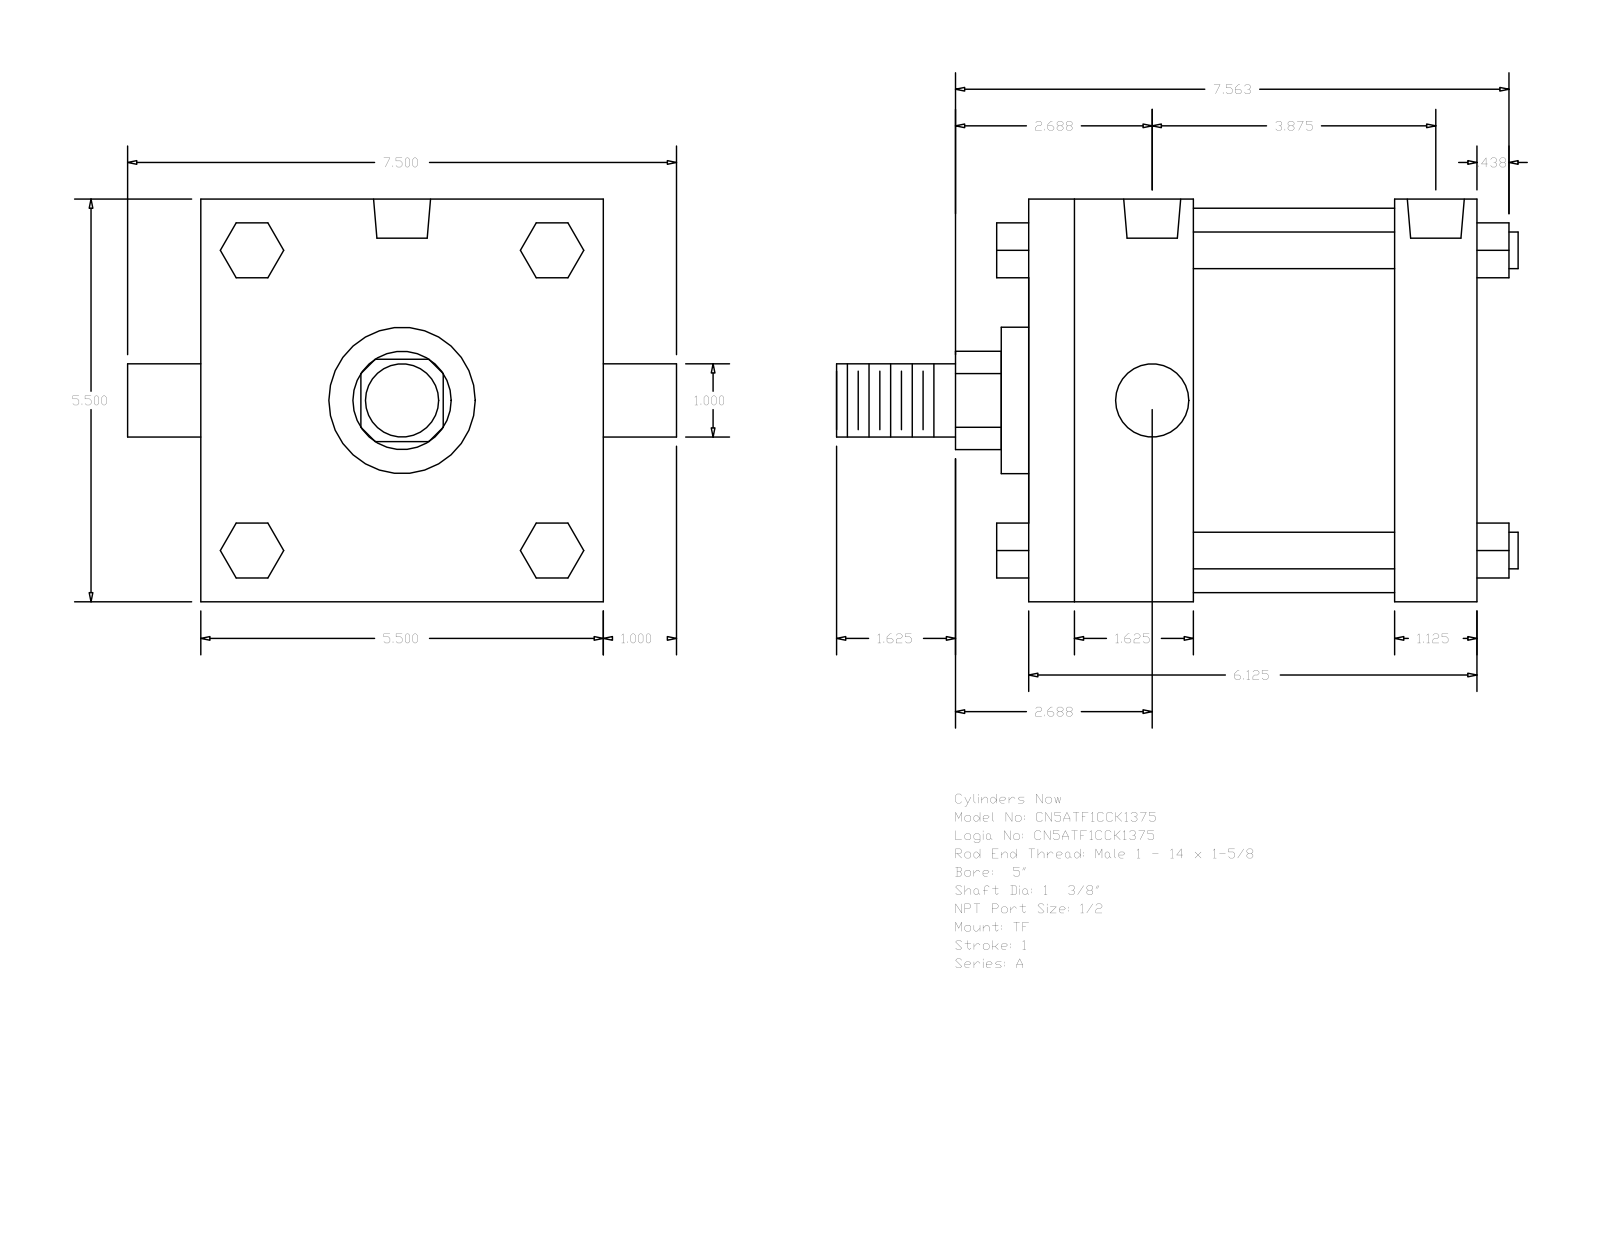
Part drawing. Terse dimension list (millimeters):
name: A_TF__0500_1.375
written by: GSSL Pune (CONFIG_CONTROL_DESIGN)
unit: mm
bodies: 0 solids, 120 faces (92 planar, 28 cylindrical, 0 other)
size: 236.54 × 190.5 × 139.7
holes: 3× ⌀8.73, 2× ⌀19.77
bosses: 4× ⌀12.7, 2× ⌀25.4, 1× ⌀133.35, 1× ⌀50.8, 1× ⌀34.92
rounds: 1× R17.06
face distances: 139.7, 155.57, 57.15, 69.85, 127, 28.57, 98.42, 19.05, 52.07, 90.18
hole spacings: 2.39, 96.04, 93.65, 98.43
